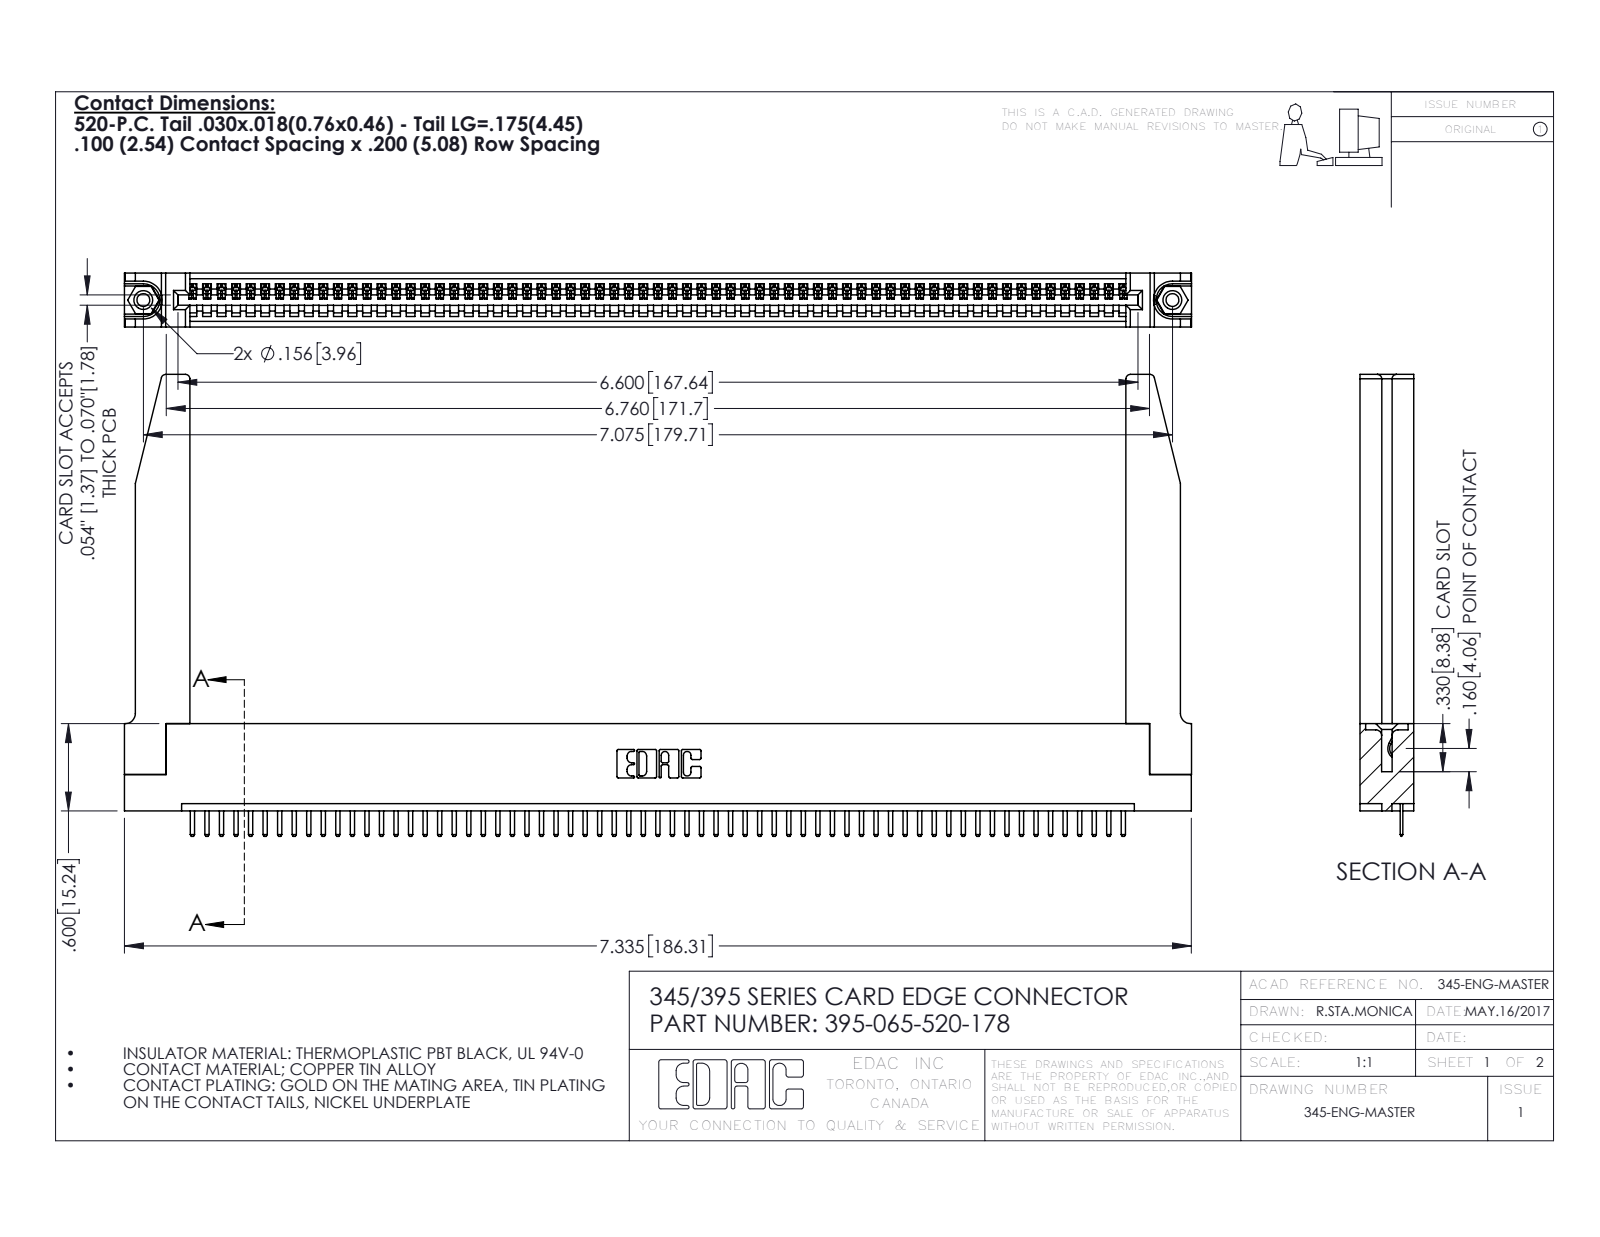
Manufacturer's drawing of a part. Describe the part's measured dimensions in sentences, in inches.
The part is named "345-250-001_345-250-001-102; 345-292-001_345-293-120; 395-065-520-178; 345 Part_Flush Mounting Lugs - 0.156 Dia-TH (+1 more)". Its 3-D file was written by "SolidWorks 2016 (CONFIG_CONTROL_DESIGN)". It is 70 solids with 4390 faces: 2952 planar, 1386 cylindrical and 52 other. Overall it measures 7.336 by 3.175 by 0.37 inches. Its volume is 1.554 cubic inches and its surface area 46.61 square inches. Round holes: 2 of diameter 0.089, 2 of diameter 0.125, 2 of diameter 0.156, 1 of diameter 0.064. Round bosses or shafts: 2 of diameter 0.155. Partial cylindrical surfaces (rounded edges, fillets, slot ends): 132 of radius 0.01, 130 of radius 0.006, 22 of radius 0.01, 8 of radius 0.03, 6 of radius 0.007, 6 of radius 0.031, 3 of radius 0.026, 2 of radius 0.031. The main face-to-face distances are 0.37, 0.072, 0.298, 0.2, 0.098, 0.272, 0.025, 0.225, 0.072, 0.148. The hole center spacings are 0.27, 6.839, 7.075.
